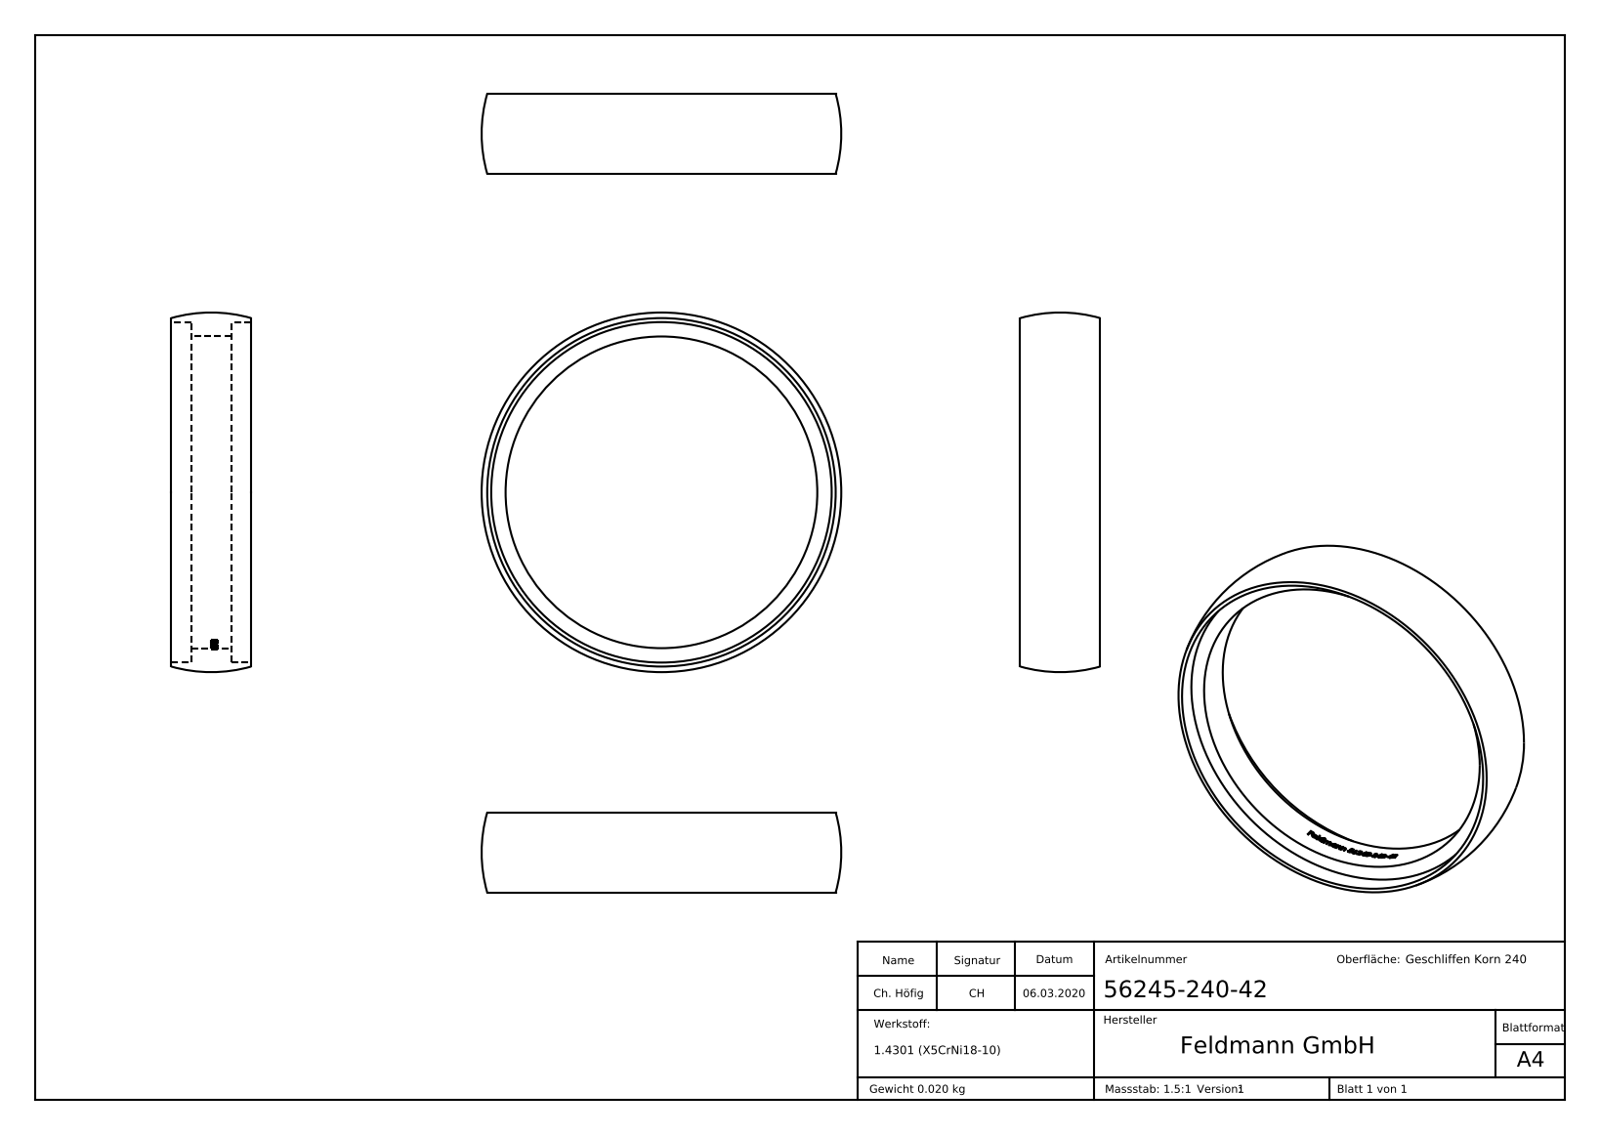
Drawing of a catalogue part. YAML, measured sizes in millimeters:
part_name: "56245-240-42"
step_written_by: "SolidWorks 2015 (CONFIG_CONTROL_DESIGN)"
units: millimeters
bodies: {solids: 1, faces: 270, planar: 138, cylindrical: 31, other: 101}
overall_size: [45, 45, 10]
volume: 2480
surface_area: 3303
round_holes:
  - {diameter: 39, count: 1}
  - {diameter: 42.6, count: 1}
partial_cylinders:
  - {radius: 19.6, count: 1}
face_to_face_distances: [5, 2.5, 7.5, 10, 2.2, 1.78, 7.78, 0.53, 0.71, 1.71]
